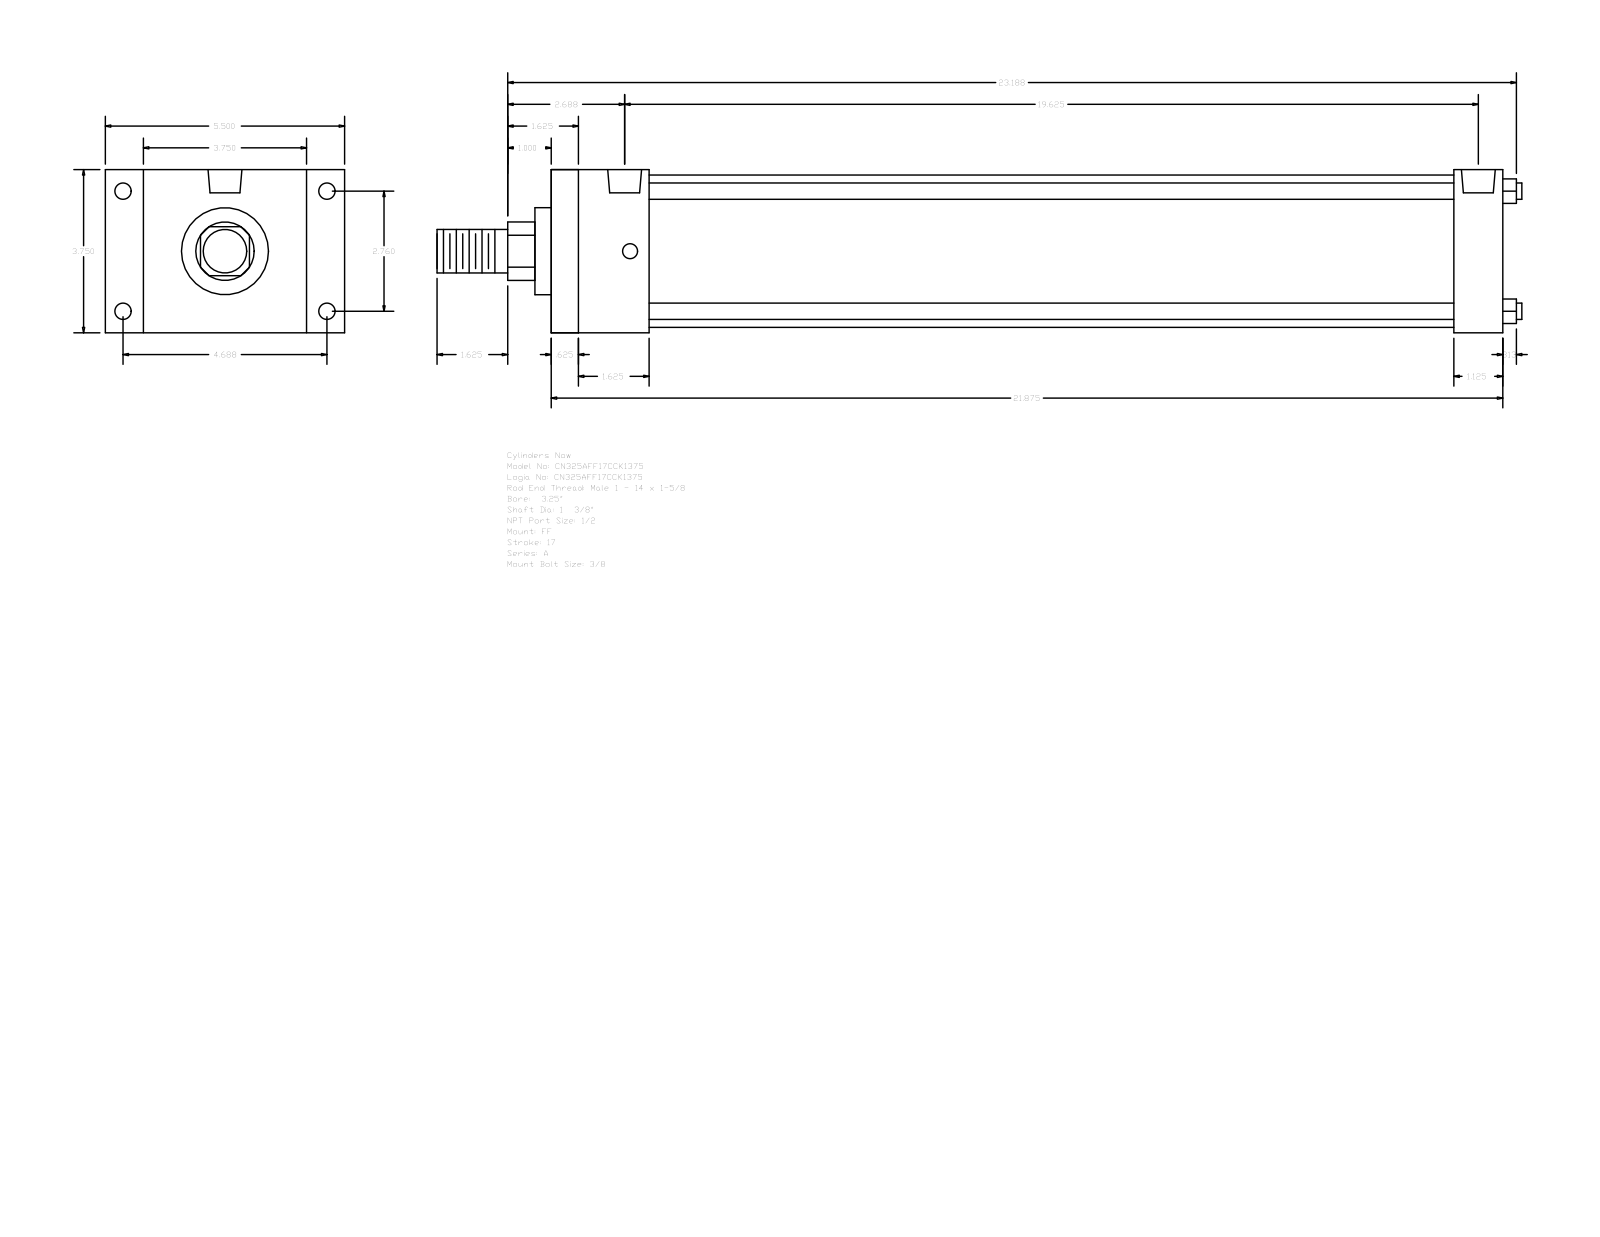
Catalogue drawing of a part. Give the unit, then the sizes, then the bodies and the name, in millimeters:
Units: millimetres
Overall size (bounding box): 633.41 × 139.7 × 95.25
Round holes (diameter × count): ⌀8.73 ×4, ⌀9.53 ×4, ⌀19.77 ×2
Round bosses / shafts (diameter × count): ⌀9.53 ×4, ⌀88.9 ×1, ⌀50.8 ×1, ⌀34.92 ×1, ⌀25.4 ×1
Partial cylindrical surfaces — rounded edges, fillets, slot ends (radius × count): R17.06 ×1
Main face-to-face distances: 95.24, 555.62, 539.75, 15.87, 57.15, 22.23, 117.47, 28.57, 527.05, 41.28
Hole centre spacings: 3.18, 70.1, 119.06, 138.16, 492.12, 495.3, 498.48
Bodies: 0 solids, 92 faces (64 planar, 28 cylindrical, 0 other)
Part name (STEP PRODUCT): A_FF__0325_1.375
STEP written by: GSSL Pune (CONFIG_CONTROL_DESIGN)
